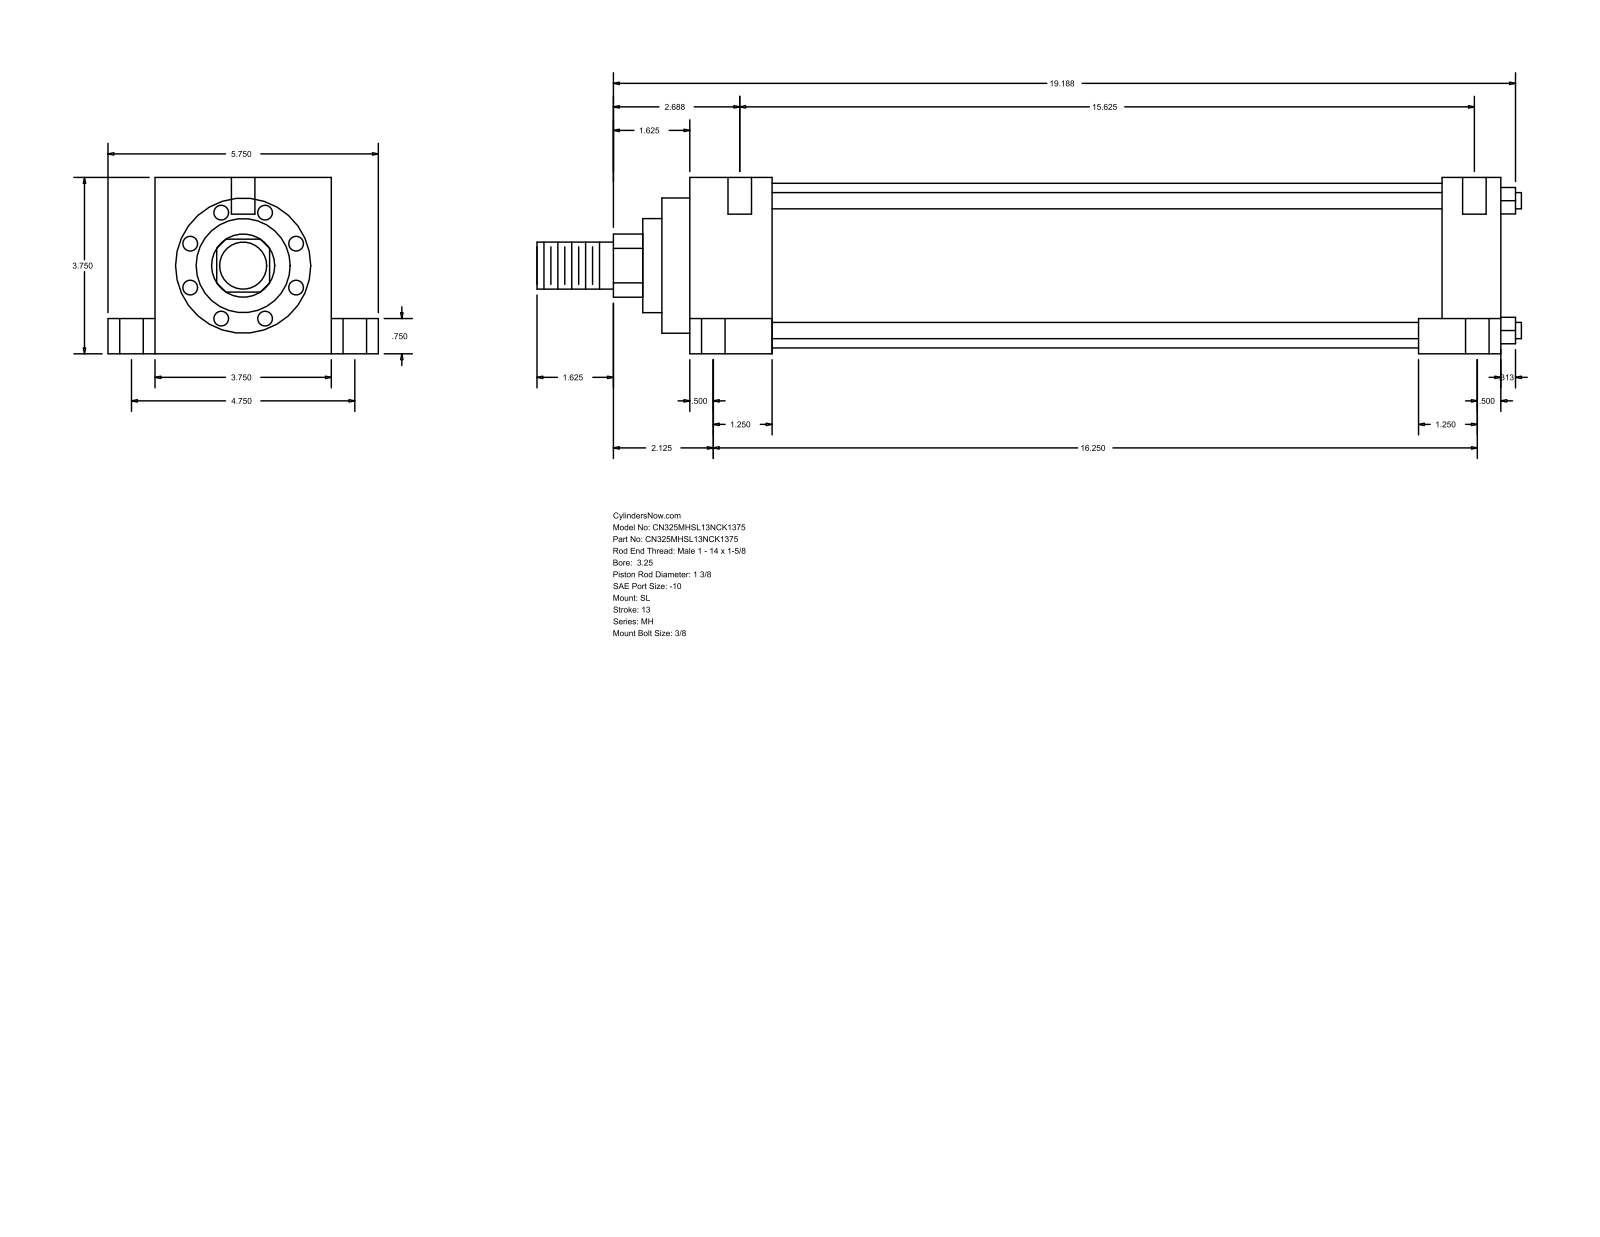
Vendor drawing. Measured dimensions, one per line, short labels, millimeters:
name: MH_SL__0325_1.375
written by: GSSL Pune (CONFIG_CONTROL_DESIGN)
unit: mm
bodies: 0 solids, 110 faces (77 planar, 33 cylindrical, 0 other)
size: 531.81 × 146.05 × 95.25
holes: 6× ⌀12.7, 4× ⌀5.56, 4× ⌀19.05
bosses: 4× ⌀8.76, 1× ⌀88.9, 1× ⌀73.03, 1× ⌀50.8, 1× ⌀34.92, 1× ⌀25.4
rounds: 1× R17.06
face distances: 95.24, 438.16, 44.45, 393.71, 25.41, 120.65, 19.05, 76.19, 406.41, 361.96
hole spacings: 60.35, 60.41, 61.65, 62, 120.66, 403.01, 403.23, 404.58
